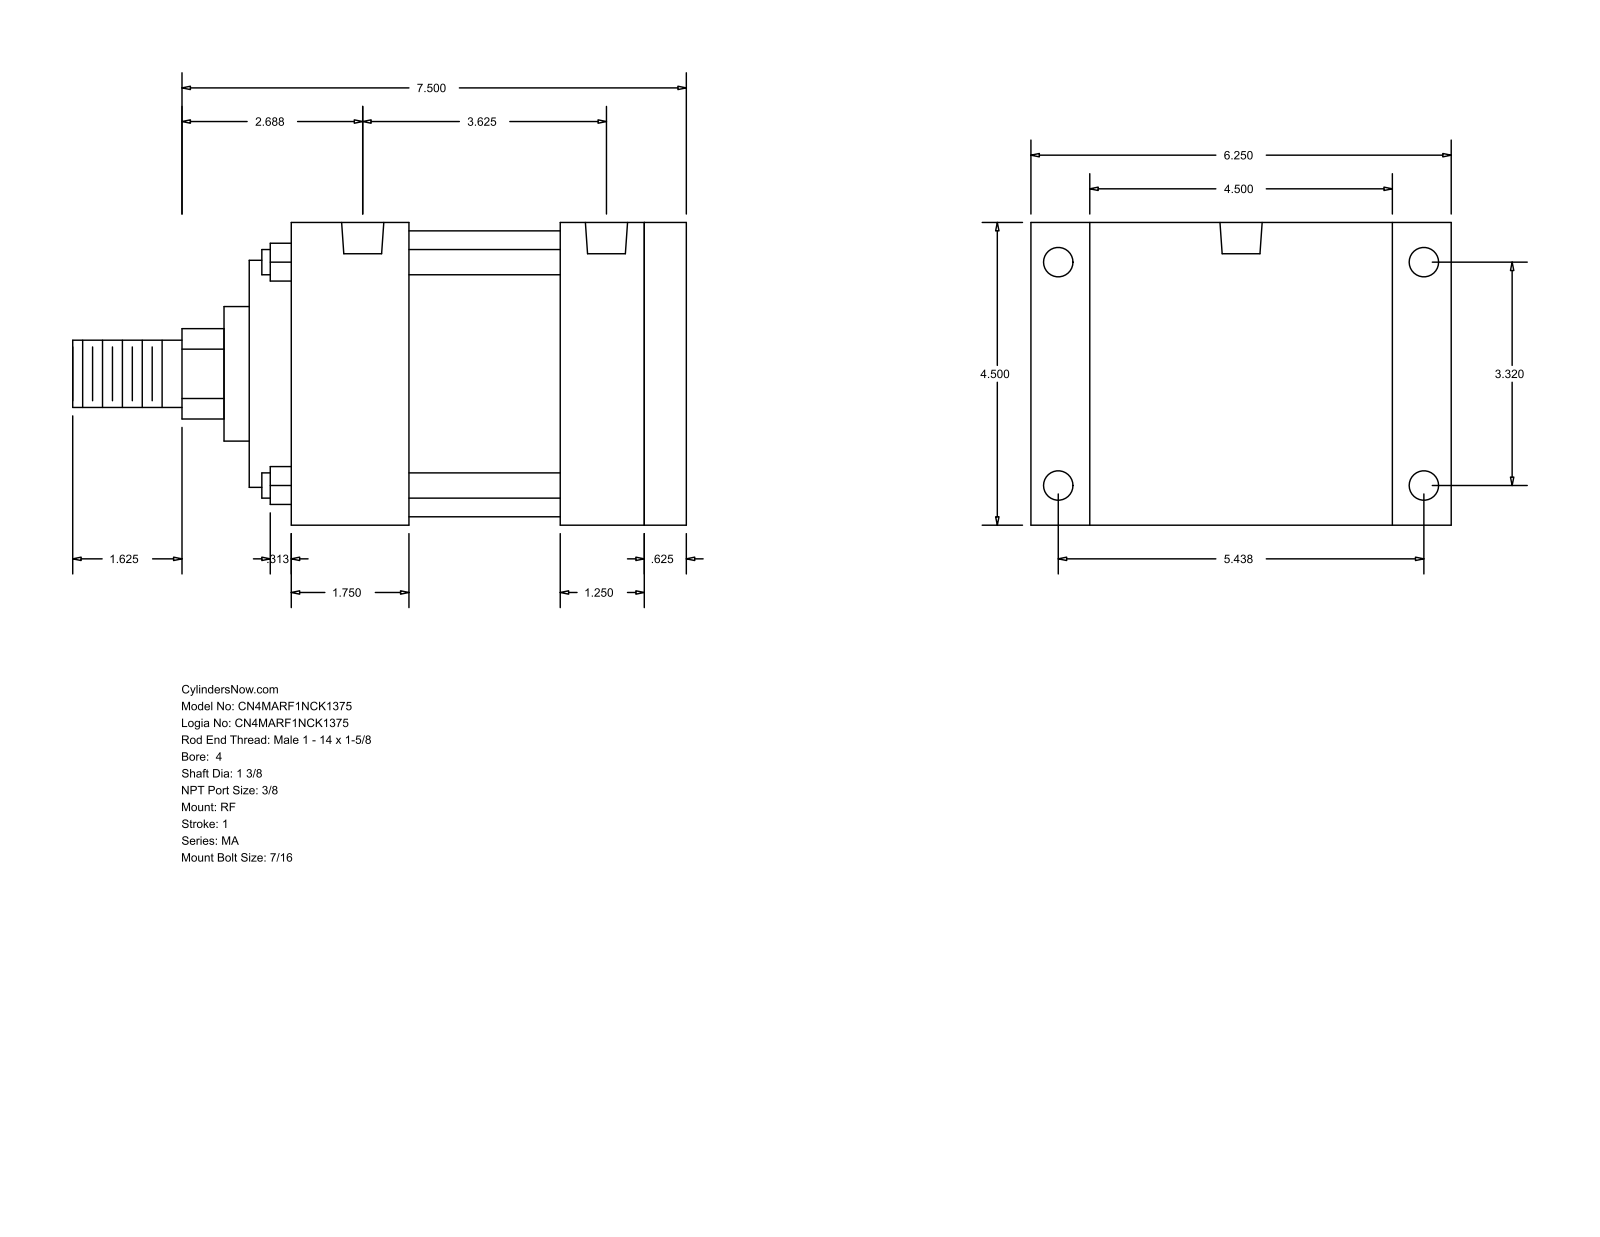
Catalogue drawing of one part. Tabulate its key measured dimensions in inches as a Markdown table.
| quantity | value |
| --- | --- |
| part name | MA_RF__0400_1.375 |
| STEP written by | GSSL Pune (CONFIG_CONTROL_DESIGN) |
| units | inches |
| bodies | 0 solids, 94 faces (65 planar, 29 cylindrical, 0 other) |
| overall size | 9.125 × 6.25 × 4.5 |
| round holes (diameter × count) | 0.437 × 8, 0.627 × 2 |
| round bosses / shafts (diameter × count) | 0.375 × 4, 4.25 × 1, 3.375 × 1, 2 × 1, 1.375 × 1, 1 × 1 |
| partial cylindrical surfaces (radius × count) | 0.672 × 1 |
| main face-to-face distances | 4.5, 5.875, 0.625, 5.25, 0.625, 5.875, 6.5, 0.875, 5.375, 4.625 |
| hole center spacings | 0.188, 3.25, 3.32, 3.437, 5.438, 6.371, 3.625 |
